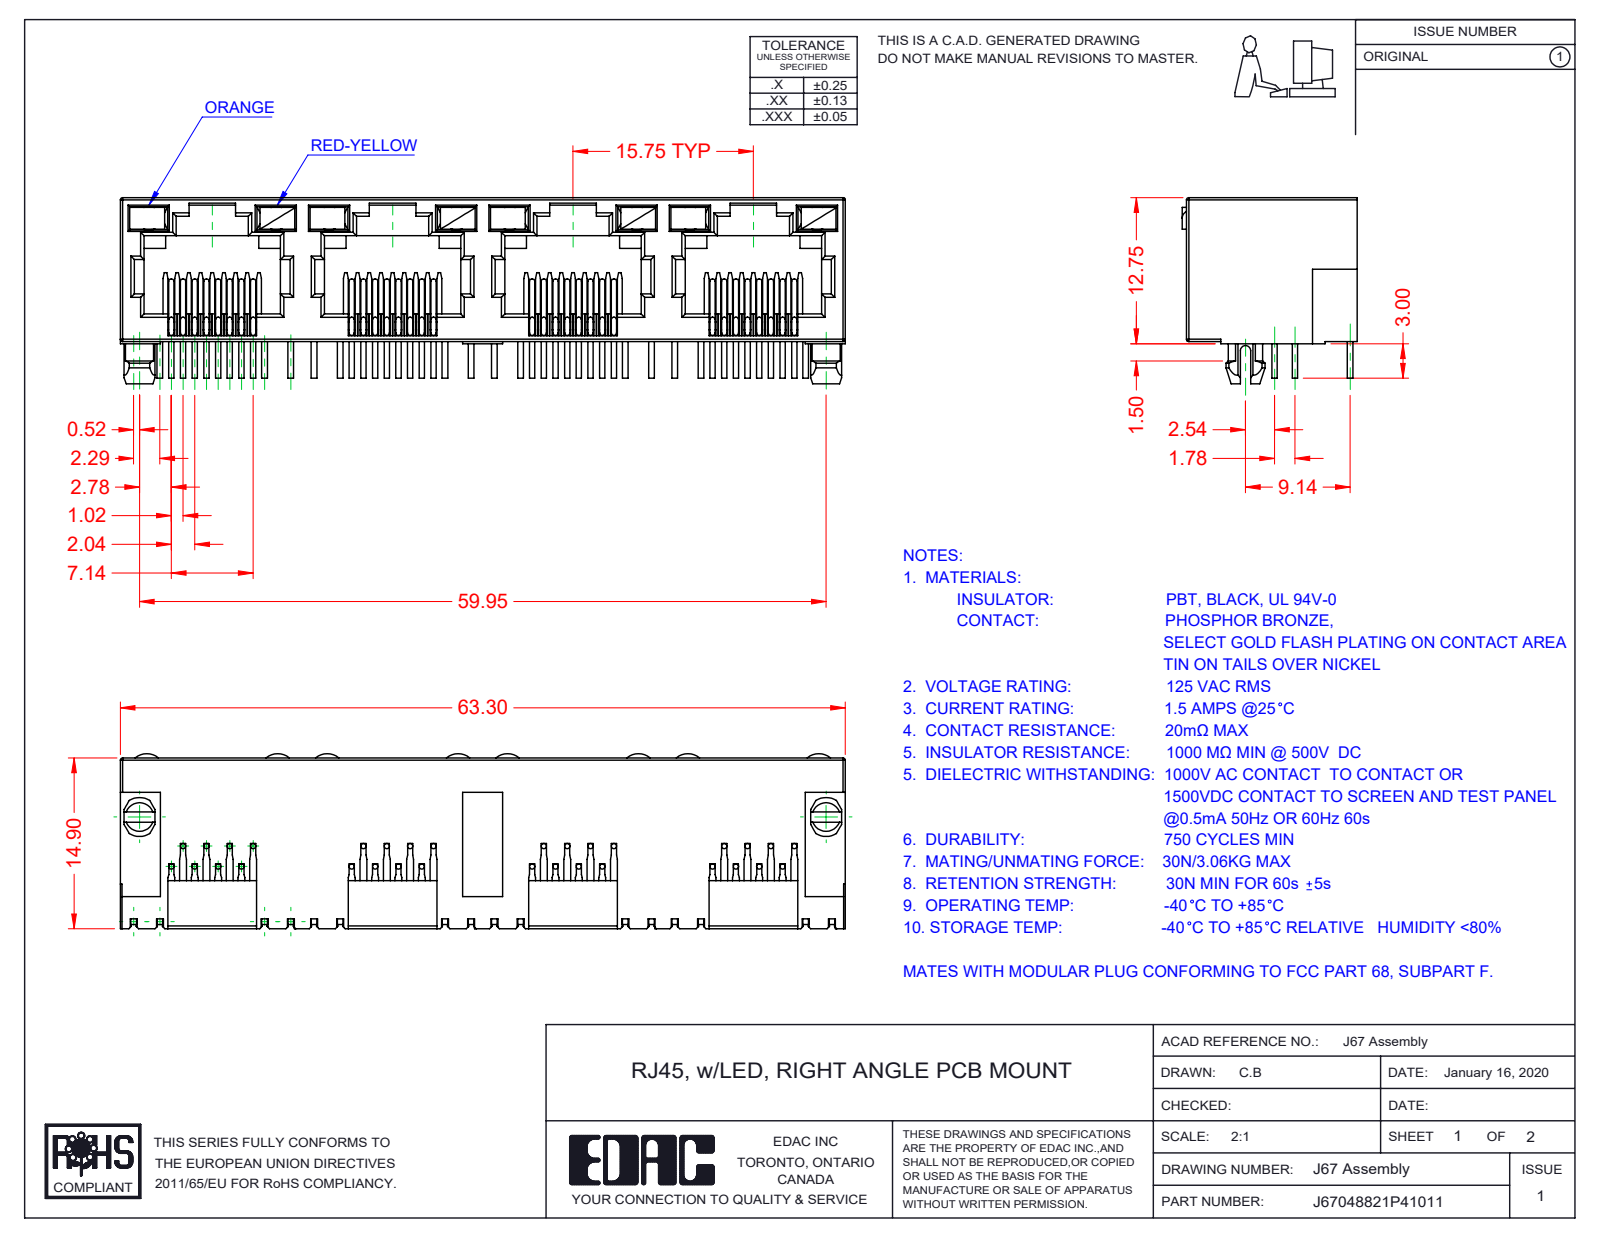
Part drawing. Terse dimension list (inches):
name: 67 Insulator; J67048822P48011; 67 LED RH_8-Red-Yellow; 67 LED LH_4-Orange (+1 more)
written by: SolidWorks 2016 (CONFIG_CONTROL_DESIGN)
unit: in
bodies: 41 solids, 2473 faces (1781 planar, 484 cylindrical, 208 other)
size: 2.492 × 0.64 × 0.602
volume: 0.315 in³; area: 17.94 in²
bosses: 96× ⌀0.018
rounds: 66× R0.008, 29× R0.012, 9× R0.018, 8× R0.061, 2× R0.059, 2× R0.067, 1× R0.014, 1× R0.039
face distances: 0.02, 0.494, 0.074, 0.035, 0.394, 0.62, 0.039, 0.055, 0.433, 0.468
